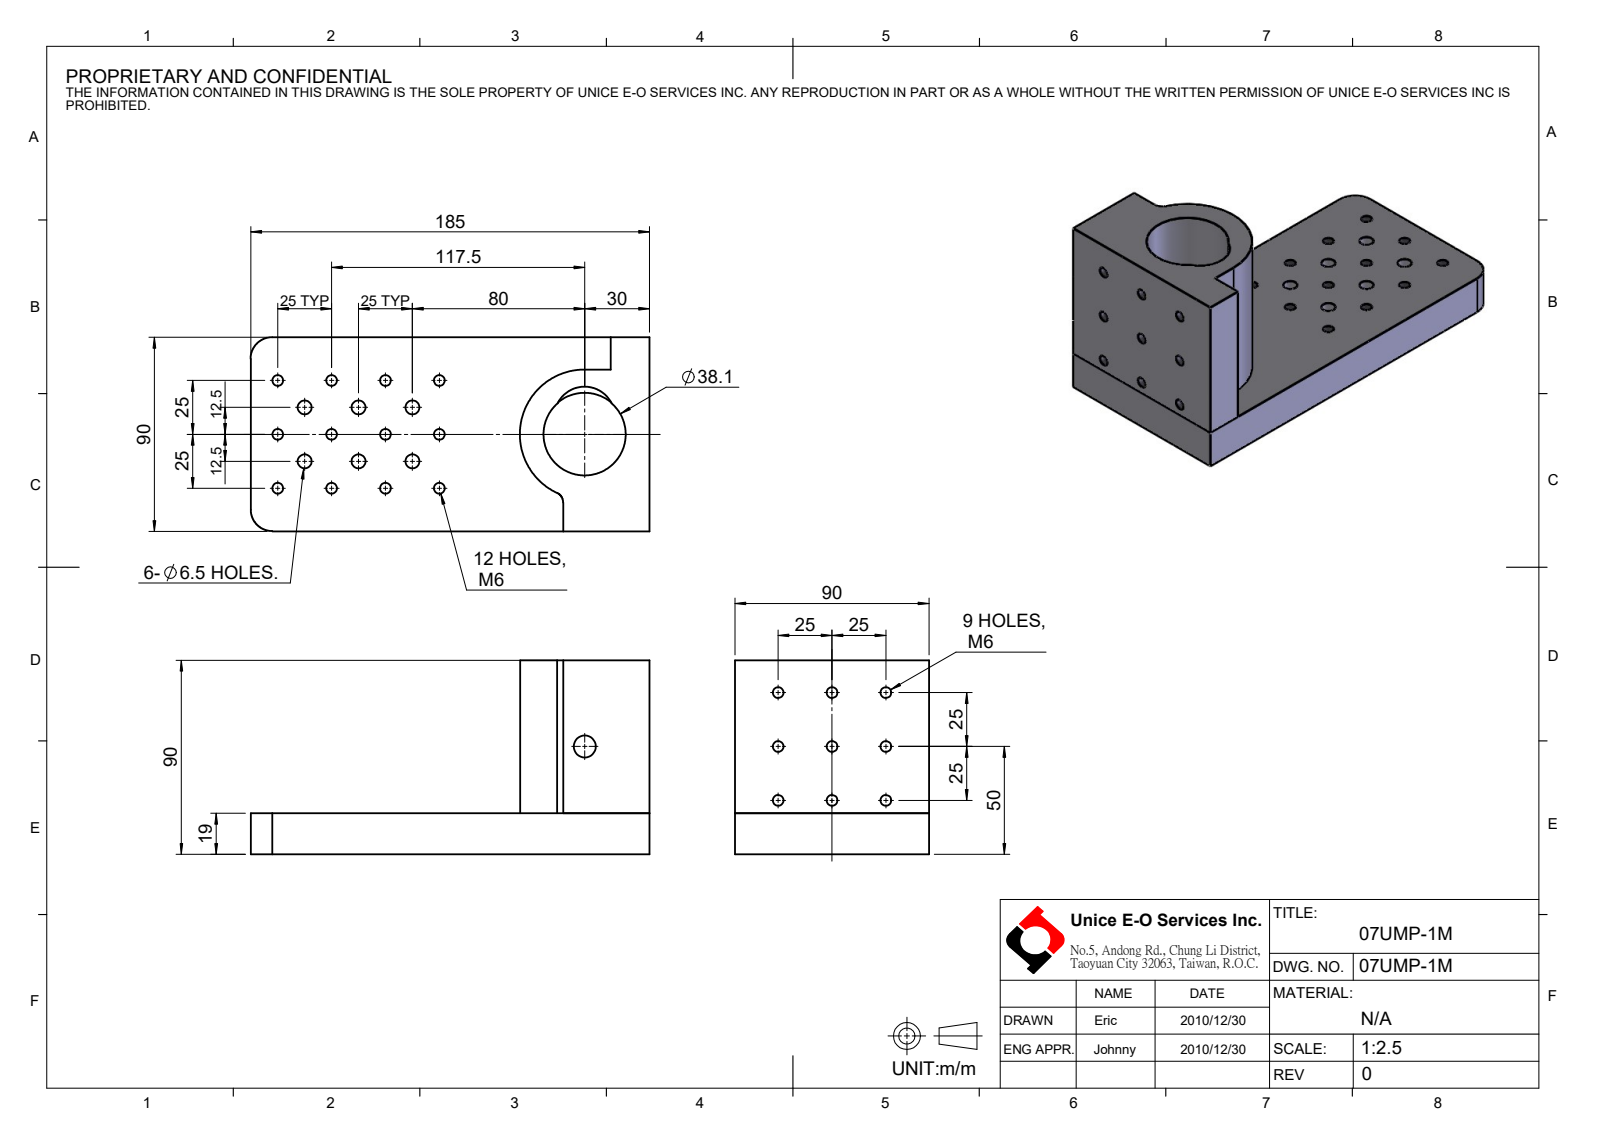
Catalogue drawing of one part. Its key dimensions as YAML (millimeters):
part_name: "07UMP-1M"
step_written_by: "SolidWorks 2016 (CONFIG_CONTROL_DESIGN)"
units: millimeters
bodies: {solids: 5, faces: 178, planar: 47, cylindrical: 95, other: 36}
overall_size: [185, 90, 90]
volume: 485963
surface_area: 87933
round_holes:
  - {diameter: 5, count: 21}
  - {diameter: 6.5, count: 6}
  - {diameter: 4.2, count: 3}
  - {diameter: 5.5, count: 3}
  - {diameter: 10, count: 3}
  - {diameter: 10.2, count: 1}
  - {diameter: 38.5, count: 1}
round_bosses_or_shafts:
  - {diameter: 8.5, count: 3}
  - {diameter: 5, count: 3}
partial_cylinders:
  - {radius: 10, count: 2}
  - {radius: 5, count: 1}
  - {radius: 14, count: 1}
  - {radius: 19.05, count: 1}
  - {radius: 30, count: 1}
face_to_face_distances: [19, 90, 71, 185, 18, 167, 40, 145, 22, 15]
hole_center_spacings: [25, 39.53, 17.68, 35.36, 55.9, 50, 53.03, 63.74]
